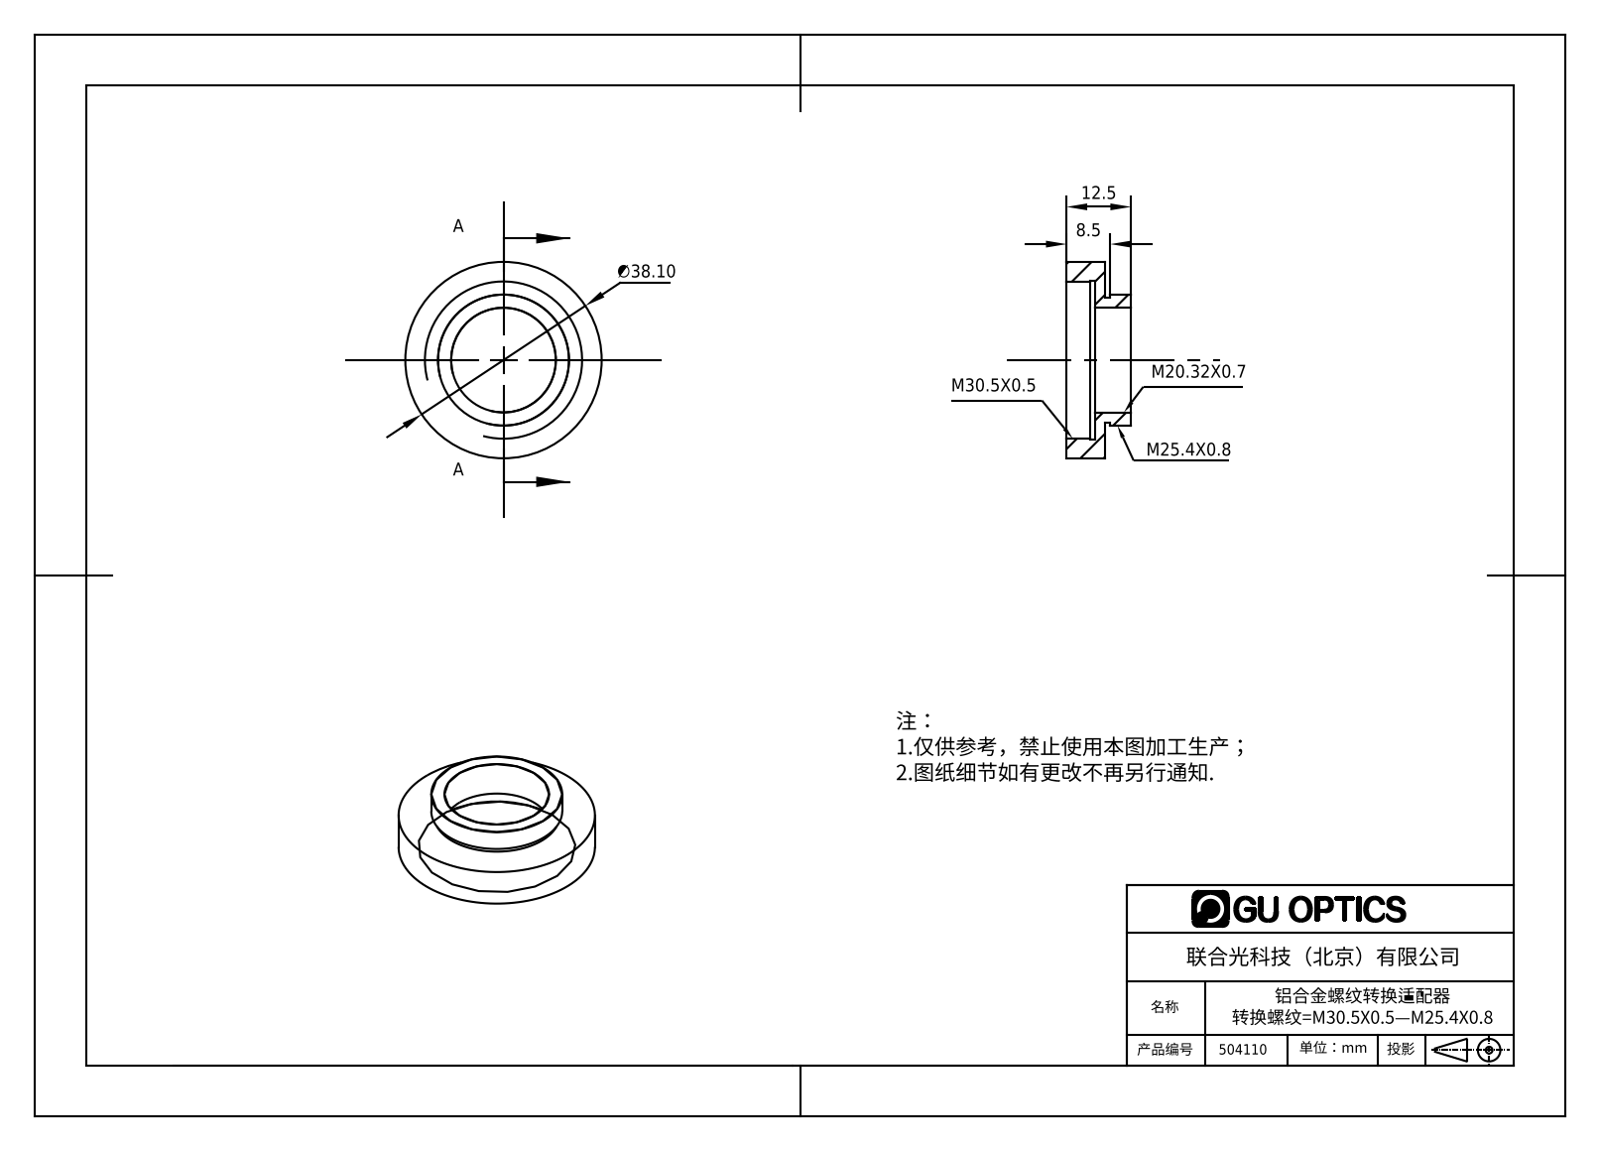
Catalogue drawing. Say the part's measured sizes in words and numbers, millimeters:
The part is named "504110". Its 3-D file was written by "SolidWorks 2016 (AUTOMOTIVE_DESIGN)". It is 1 solid with 18 faces: 6 planar, 12 cylindrical and 0 other. Overall it measures 38.1 by 38.1 by 12.5 millimeters. Its volume is 4 759 cubic millimeters and its surface area 4 001 square millimeters. Round holes: 1 of diameter 20.3, 1 of diameter 30.48, 1 of diameter 30.7. Round bosses or shafts: 1 of diameter 38.1, 1 of diameter 25.42, 1 of diameter 24.4. The main face-to-face distances are 2, 5.5, 7.5, 12.5, 7, 5, 1, 3, 4, 8.5.
